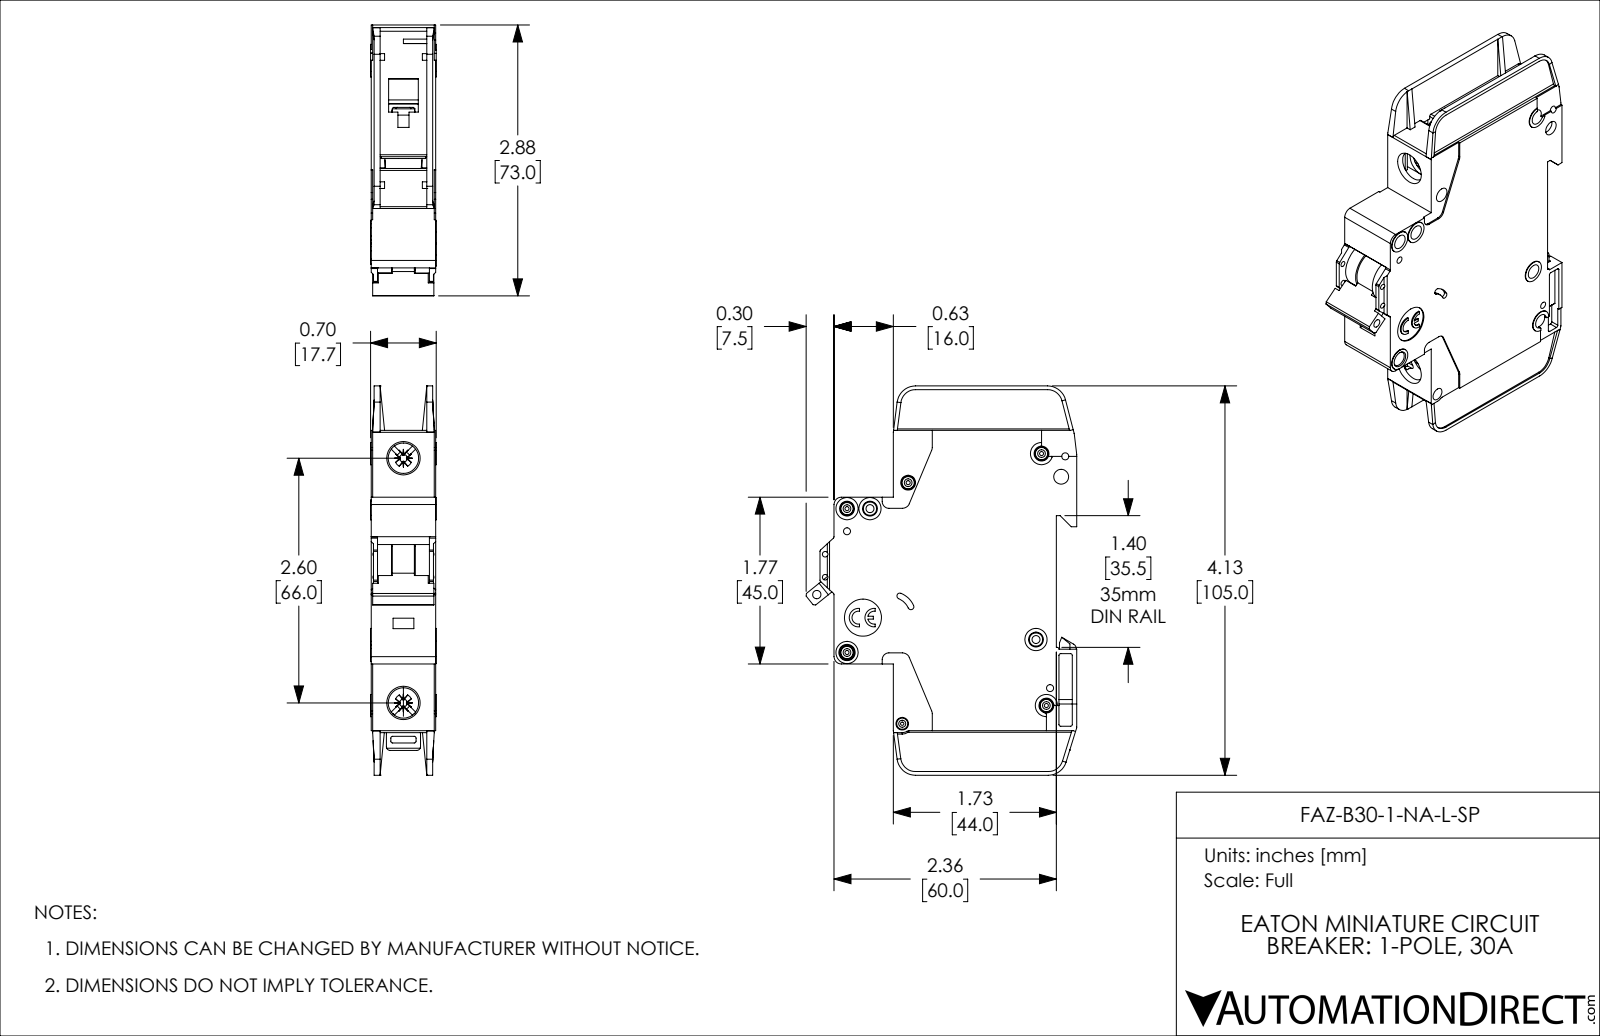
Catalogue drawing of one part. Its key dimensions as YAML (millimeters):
part_name: "FAZ-B30-1-NA-L-SP"
step_written_by: "SolidWorks 2019 (AUTOMOTIVE_DESIGN)"
units: millimeters
bodies: {solids: 1, faces: 1127, planar: 671, cylindrical: 357, other: 99}
overall_size: [105, 73.1, 17.7]
volume: 76720
surface_area: 26460
round_holes:
  - {diameter: 4, count: 8}
  - {diameter: 1.1, count: 5}
  - {diameter: 1.9, count: 4}
  - {diameter: 1.5, count: 2}
  - {diameter: 2.2, count: 2}
  - {diameter: 8.2, count: 2}
  - {diameter: 0.9, count: 1}
  - {diameter: 2.3, count: 1}
  - {diameter: 2.5, count: 1}
  - {diameter: 3.4, count: 1}
  - {diameter: 10, count: 1}
round_bosses_or_shafts:
  - {diameter: 3.3, count: 5}
  - {diameter: 6, count: 4}
  - {diameter: 3, count: 2}
  - {diameter: 2.5, count: 1}
partial_cylinders:
  - {radius: 0.5, count: 42}
  - {radius: 0.4, count: 10}
  - {radius: 1, count: 10}
  - {radius: 2, count: 8}
  - {radius: 5, count: 5}
  - {radius: 0.2, count: 4}
  - {radius: 0.7, count: 4}
  - {radius: 1.1, count: 4}
face_to_face_distances: [1.2, 17.4, 15, 16.2, 2.4, 13.8, 0.4, 0.8, 12.6, 14.6]
hole_center_spacings: [6.2, 13.6, 22.1, 4.8, 5.1, 5.2, 5.6, 6.1]
